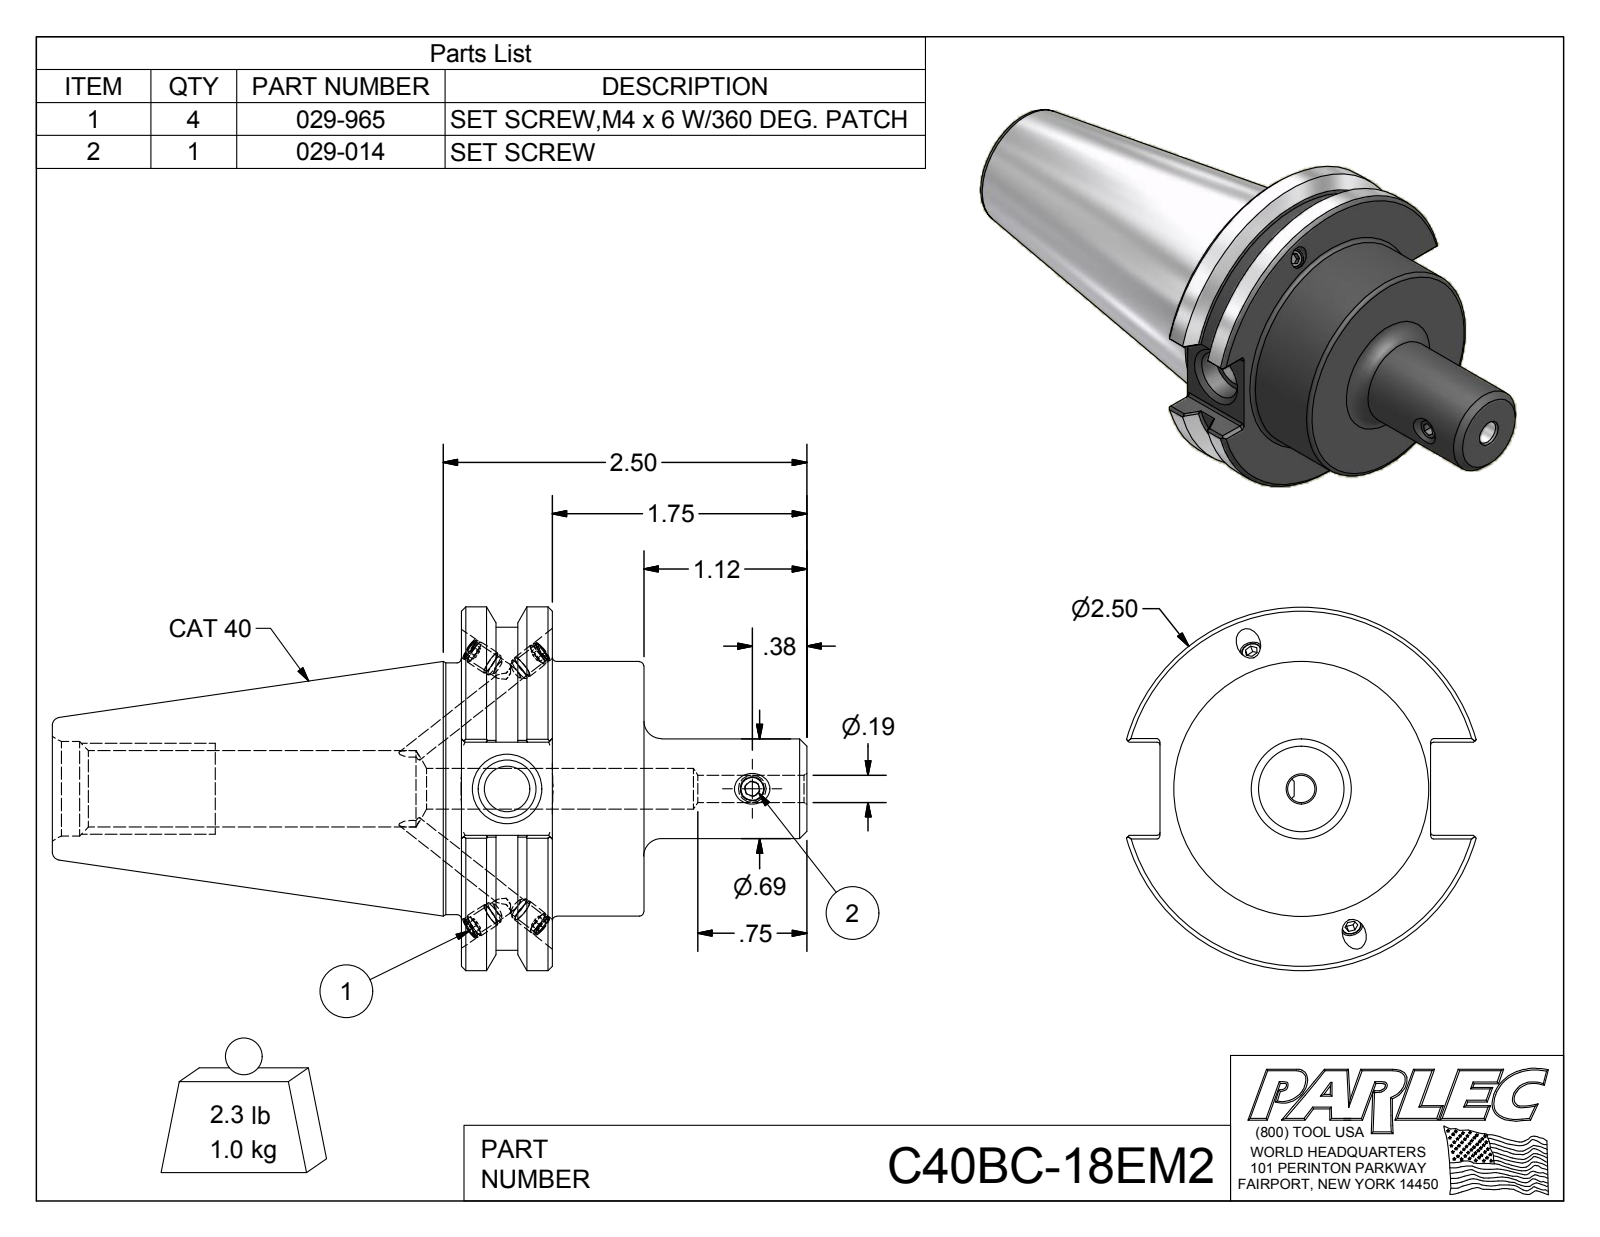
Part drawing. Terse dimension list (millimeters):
name: C40BC-18EM2; C40BC-18EM2-1; 029-014; 029-965
written by: Autodesk Inventor 2012 (AUTOMOTIVE_DESIGN)
unit: mm
bodies: 6 solids, 184 faces (85 planar, 49 cylindrical, 50 other)
size: 131.7 × 63.5 × 61.1
volume: 132 600 mm³; area: 25 780 mm²
holes: 4× ⌀3.3, 4× ⌀4.1, 1× ⌀4, 1× ⌀4.7, 1× ⌀7.1, 1× ⌀8, 1× ⌀10.1, 1× ⌀13.4, 1× ⌀16.5
bosses: 4× ⌀4.2, 4× ⌀4, 1× ⌀63.5, 1× ⌀56.4, 1× ⌀44.5, 1× ⌀43.9, 1× ⌀17.4, 1× ⌀4.8
rounds: 12× R0.5
face distances: 15.9, 31.9, 16, 60.3, 44.5, 28.4, 16.3, 47.2, 71.4, 87.3
hole spacings: 42.8
